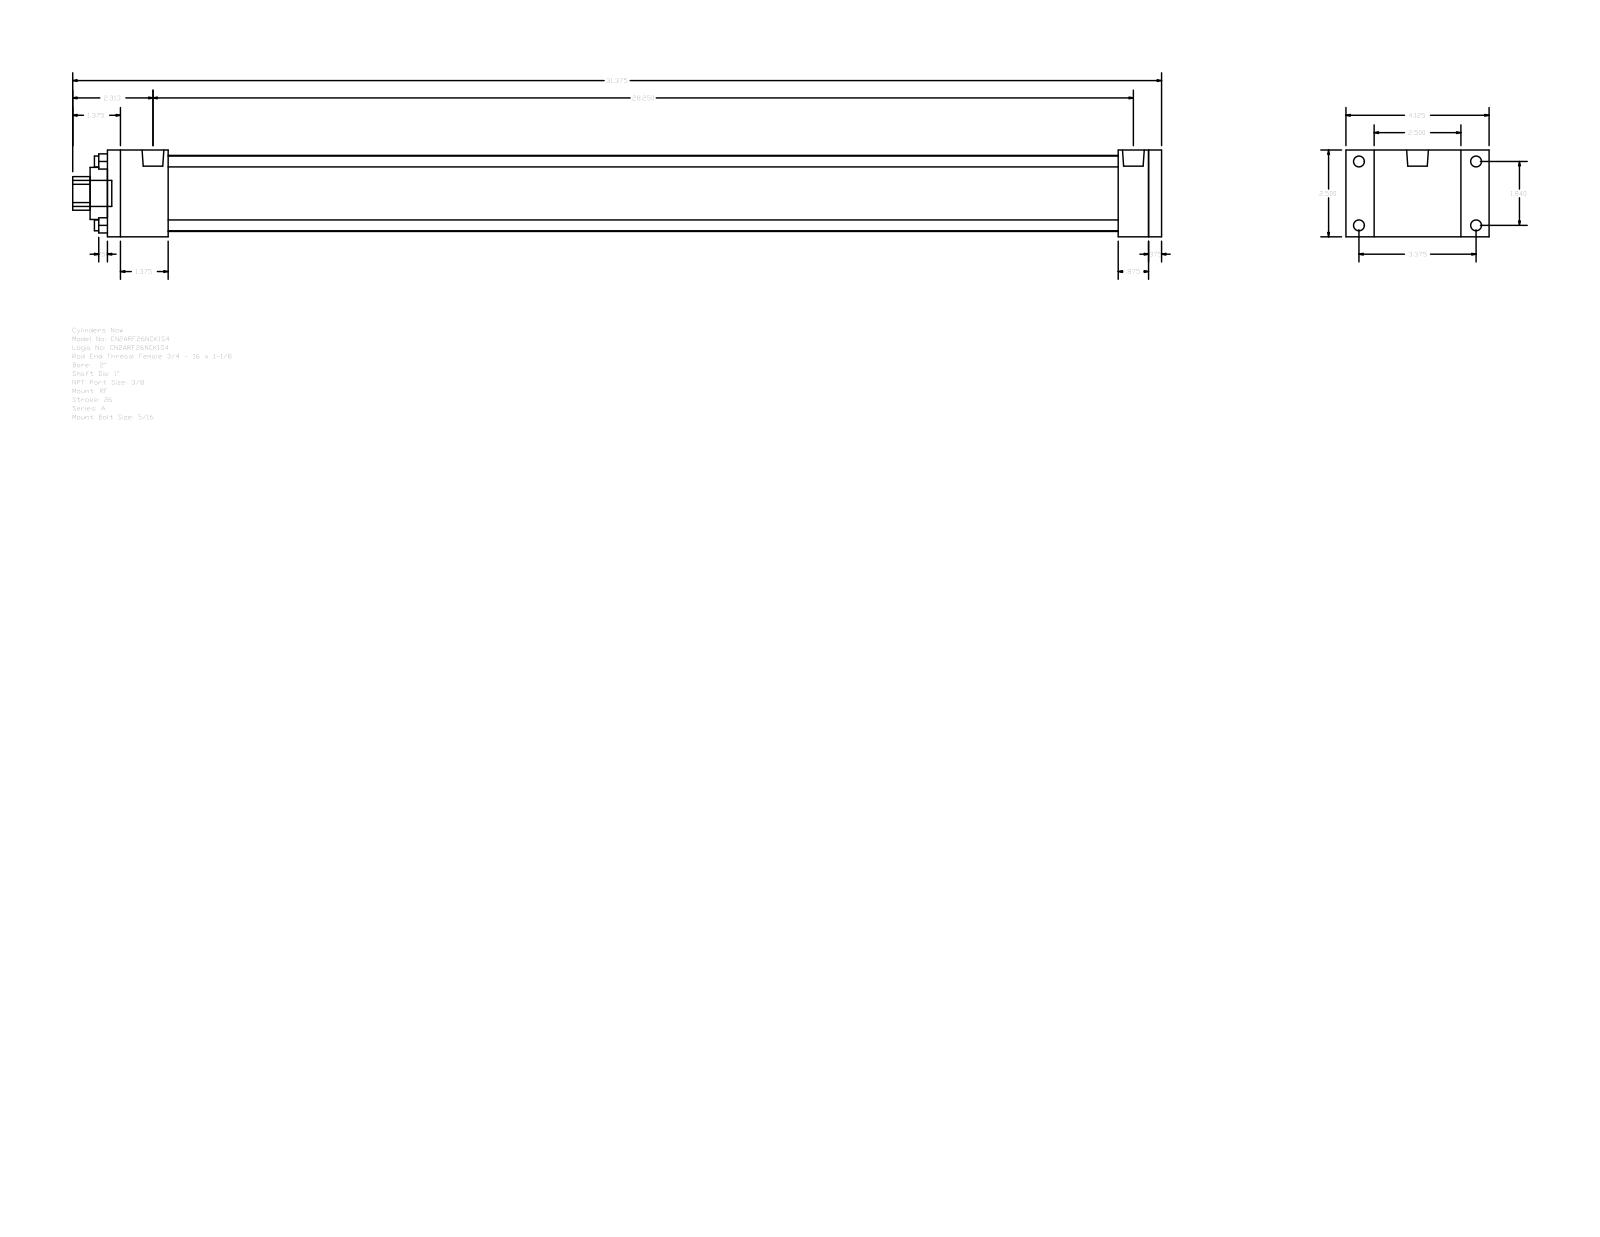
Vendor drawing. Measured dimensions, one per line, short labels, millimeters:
name: A_RF__0200_1
written by: GSSL Pune (CONFIG_CONTROL_DESIGN)
unit: mm
bodies: 0 solids, 92 faces (64 planar, 28 cylindrical, 0 other)
size: 796.92 × 104.78 × 63.5
holes: 4× ⌀7.94, 1× ⌀25.4, 1× ⌀38.1, 1× ⌀55.63
bosses: 4× ⌀7.94, 4× ⌀5.56, 2× ⌀15.93, 1× ⌀19.05
rounds: 1× R12.29
face distances: 63.5, 9.52, 771.52, 762, 20.64, 44.45, 717.55, 727.07, 739.77, 695.32
hole spacings: 33.05, 46.74, 66.1
